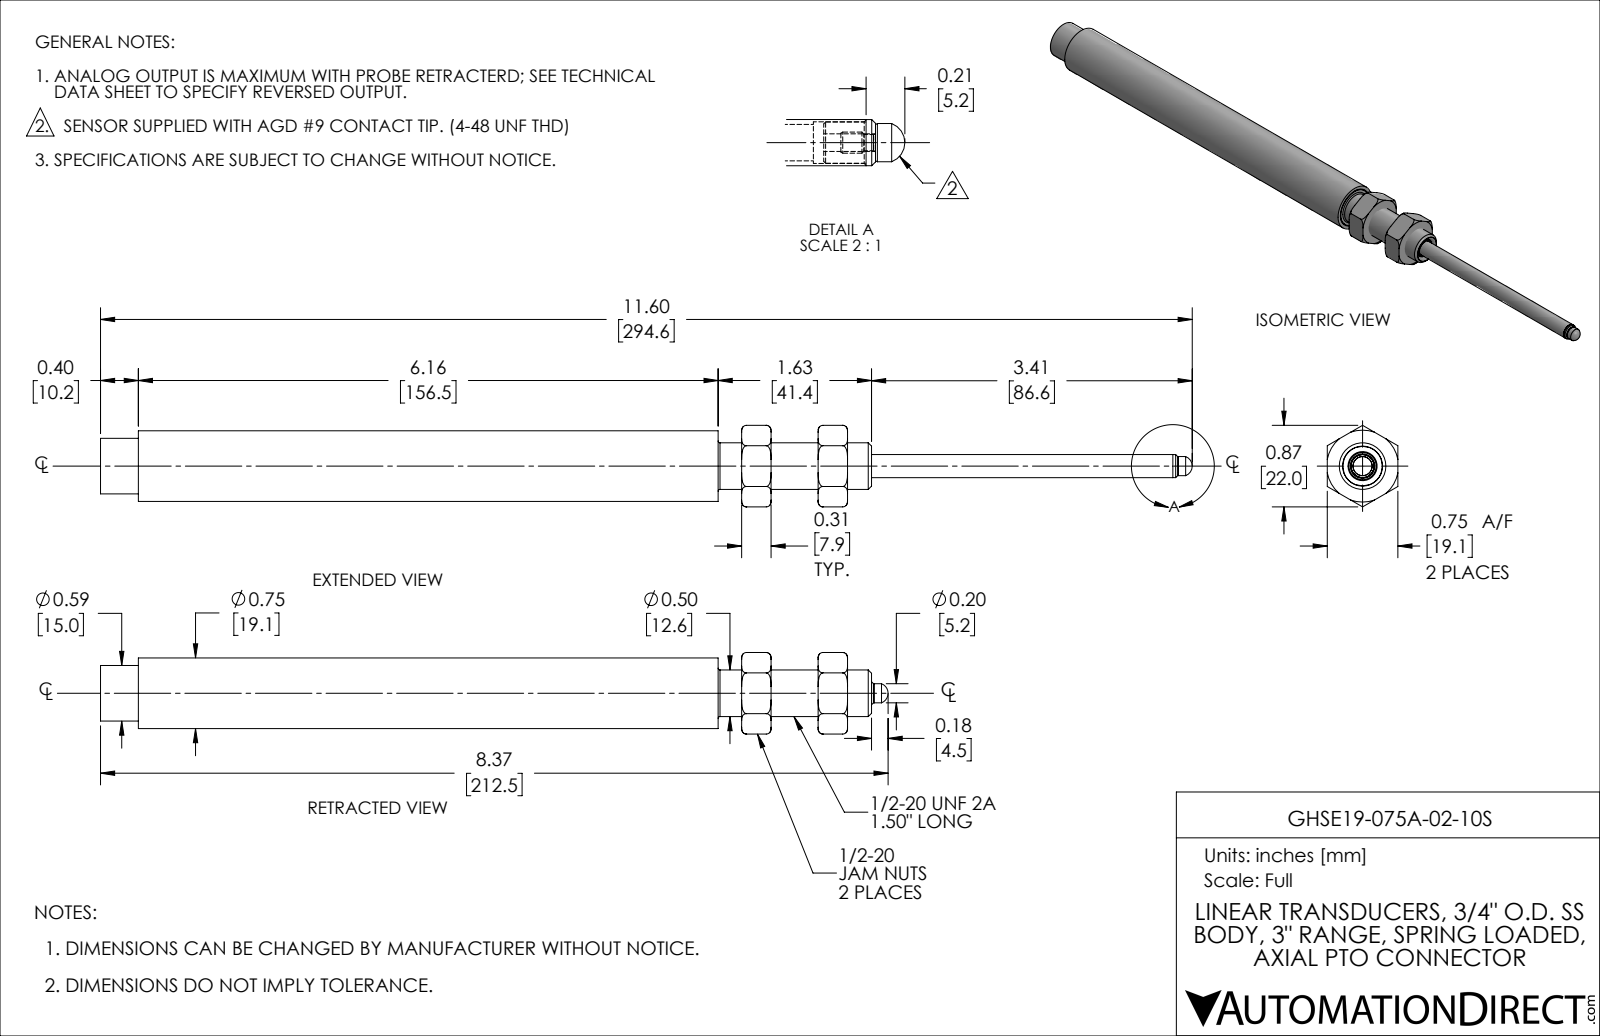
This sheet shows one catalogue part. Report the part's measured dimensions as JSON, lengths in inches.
{"part_name": "GHSE19-075A-02-10S", "step_written_by": "SolidWorks 2019 (CONFIG_CONTROL_DESIGN)", "units": "inches", "bodies": {"solids": 11, "faces": 187, "planar": 77, "cylindrical": 65, "other": 45}, "overall_size": [8.368, 0.866, 0.75], "volume_in3": 1.611, "surface_area_in2": 51.51, "round_holes": [[0.093, 1], [0.156, 1], [0.193, 1], [0.221, 1], [0.249, 1], [0.302, 1], [0.31, 1], [0.453, 1], [0.52, 1], [0.62, 1], [0.625, 1], [0.65, 1]], "round_bosses_or_shafts": [[0.03, 6], [0.75, 1], [0.725, 1], [0.672, 1], [0.624, 1], [0.59, 1], [0.495, 1], [0.375, 1]], "partial_cylinders_radius": [[0.011, 2], [0.04, 2], [0.133, 1], [0.156, 1], [0.275, 1]], "face_to_face_distances": [0.813, 0.313, 0.75, 1.125, 0.5, 0.75, 6.432, 6.744, 7.244, 7.557]}
